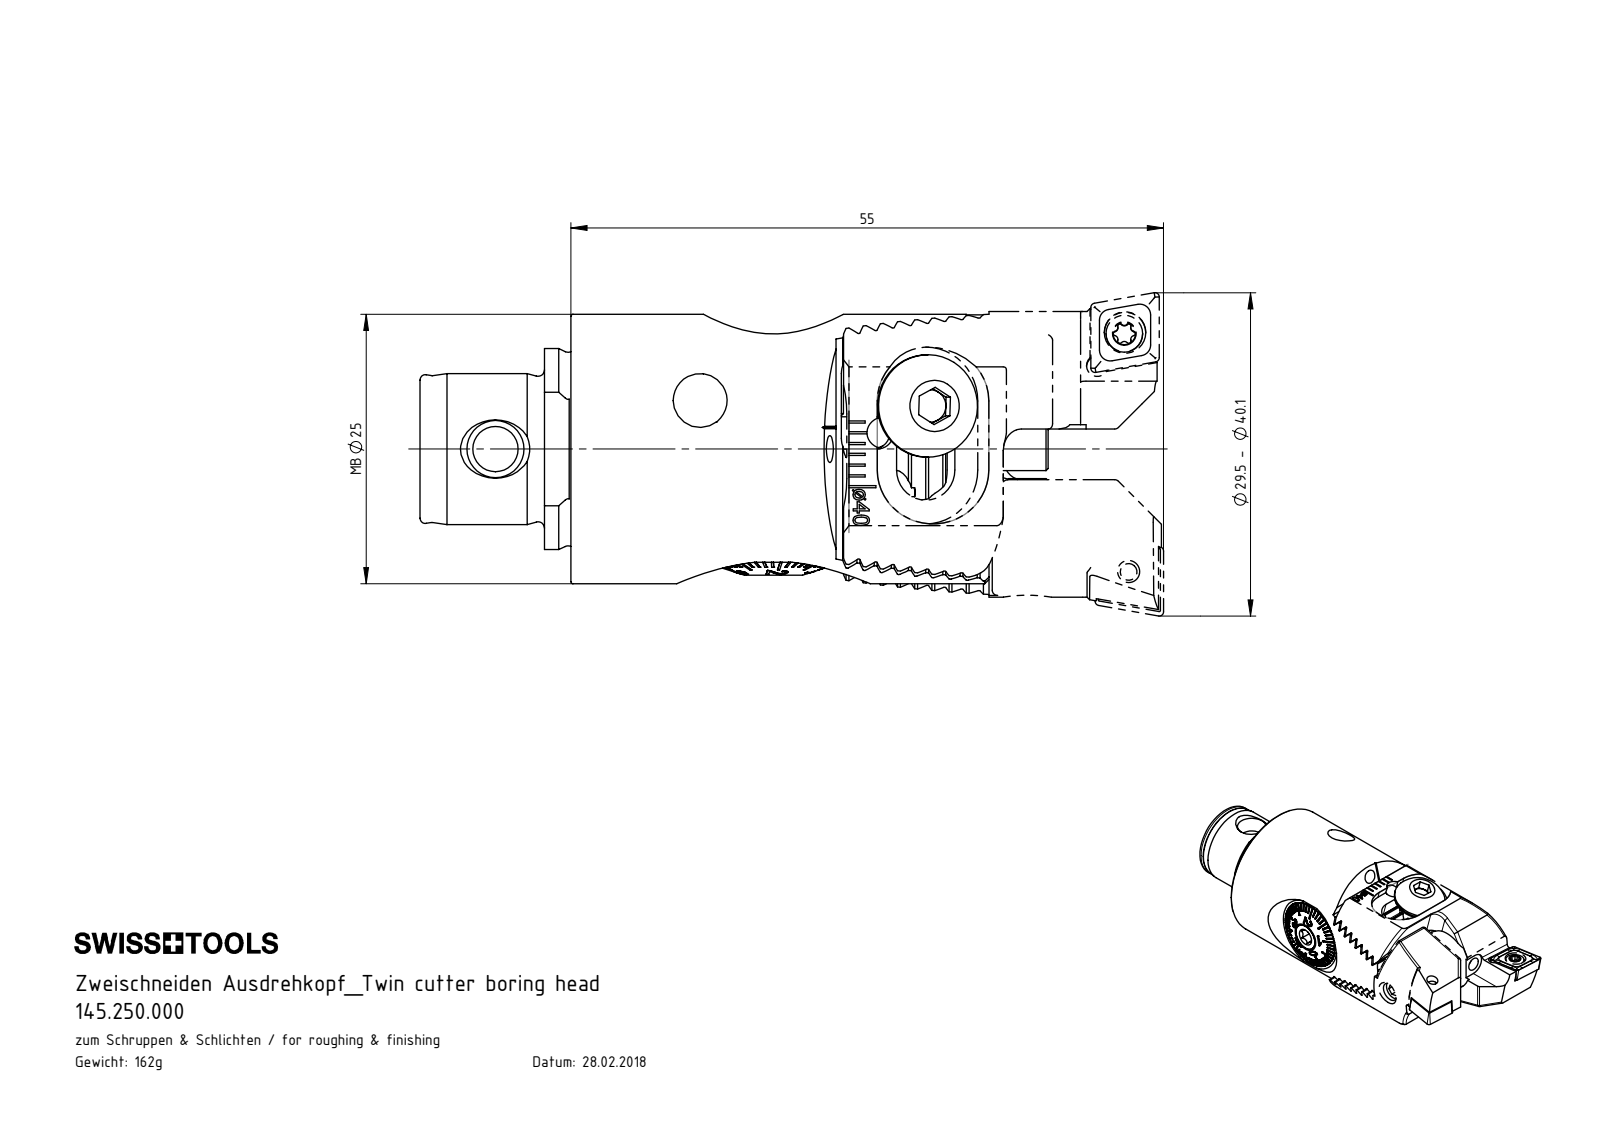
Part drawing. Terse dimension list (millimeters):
name: DIN 3771 - 11x1; Z25-ER1.001.012; F25-BG2.013.004_A; Z25-ER1.003.012_A_gespannt (+8 more)
written by: SolidWorks 2017 (CONFIG_CONTROL_DESIGN)
unit: mm
bodies: 23 solids, 1483 faces (736 planar, 296 cylindrical, 451 other)
size: 69 × 30 × 25
volume: 21 302 mm³; area: 15 967 mm²
holes: 4× ⌀2.5, 3× ⌀2, 3× ⌀4.2, 3× ⌀5, 2× ⌀1.6, 2× ⌀2.05, 2× ⌀2.8, 2× ⌀3, 2× ⌀3.85, 2× ⌀5.3, 2× ⌀6, 1× ⌀2.4
bosses: 3× ⌀3, 2× ⌀9.5, 2× ⌀9.2, 2× ⌀5, 2× ⌀4.95, 2× ⌀4, 2× ⌀3.4, 2× ⌀2.5
rounds: 19× R0.5, 18× R0.12, 16× R0.12, 12× R0.21, 10× R0.36, 5× R2, 4× R2.8, 4× R5
face distances: 1.43, 2.86, 1.39, 1.47, 4.29, 7.14, 2.9, 5.71, 8.57, 5.72
hole spacings: 3.91, 4.01, 22.47, 4.2, 6.02, 7, 15, 16.41
